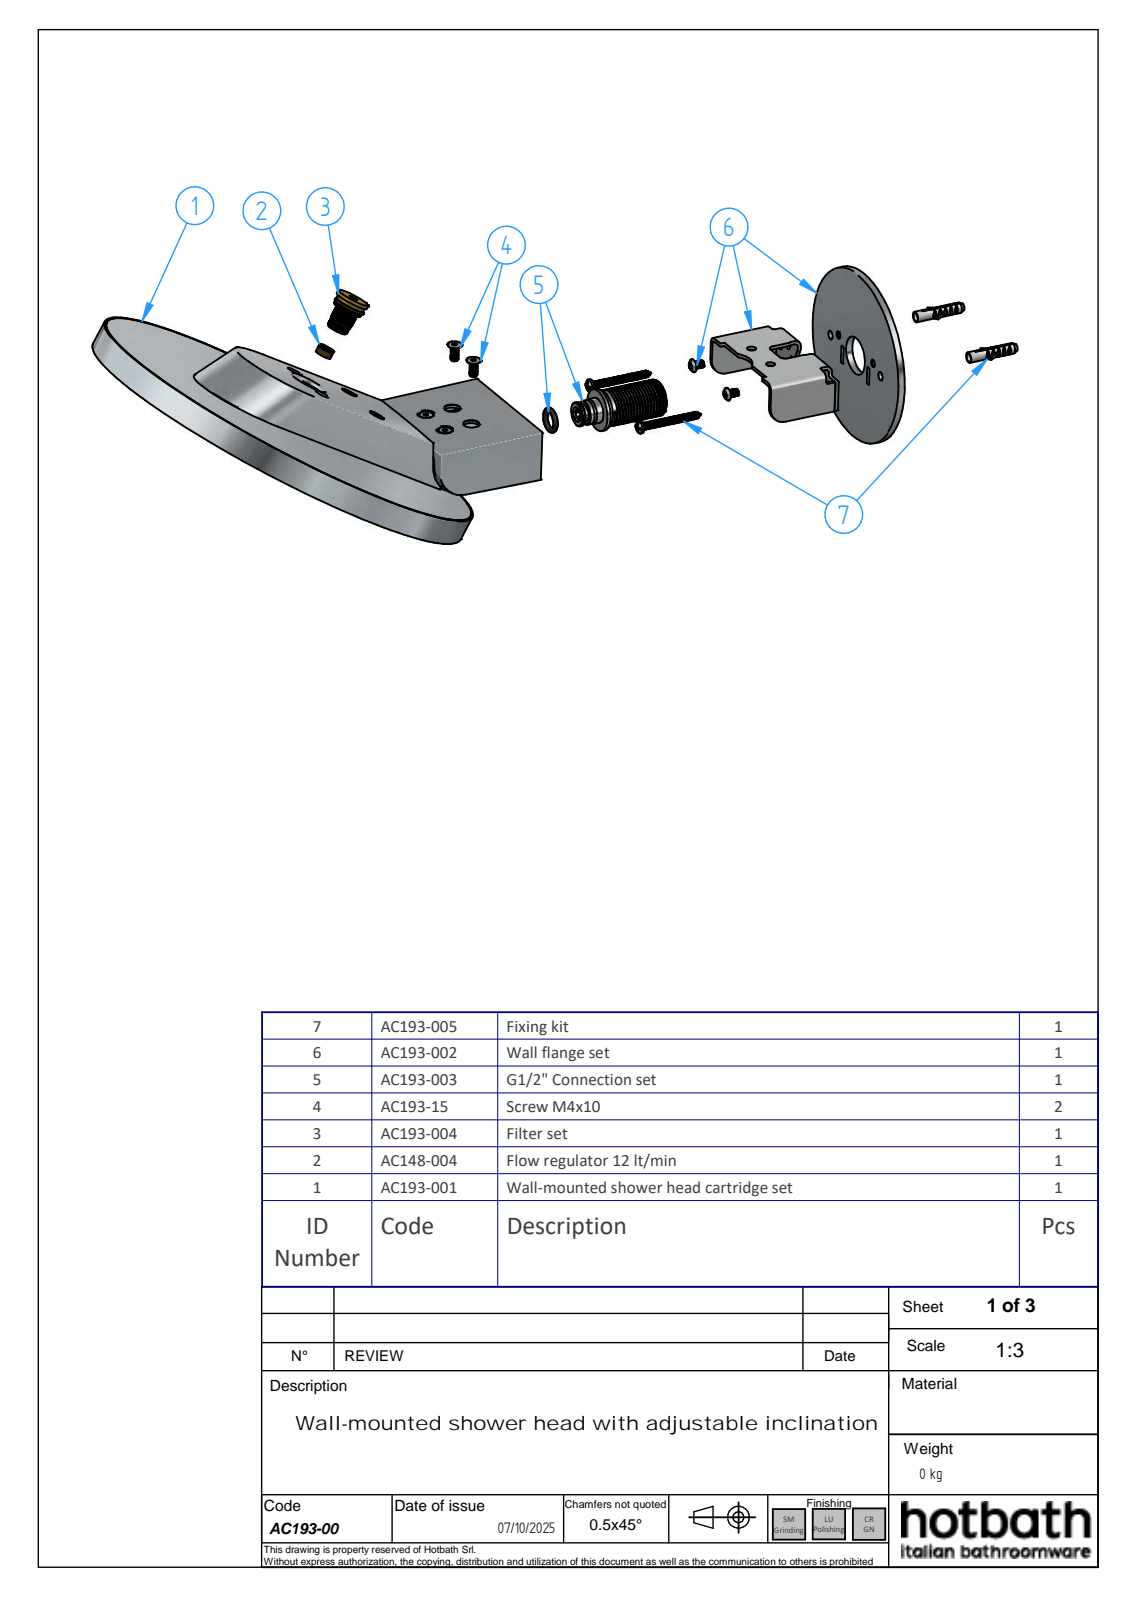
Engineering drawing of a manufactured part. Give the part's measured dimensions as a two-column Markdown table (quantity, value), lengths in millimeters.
| quantity | value |
| --- | --- |
| part name | AC193-00; E044301_28600SC_ASM_1_ASM_oa_0; C073084_068D3ZZ_1; C130044_068D3ZZ_1 (+8 more) |
| STEP written by | Solid Edge (AUTOMOTIVE_DESIGN) |
| units | millimeters |
| bodies | 22 solids, 14013 faces (3144 planar, 1624 cylindrical, 9245 other) |
| overall size | 252.75 × 232 × 143 |
| volume | 689 760 mm³ |
| surface area | 564 044 mm² |
| round holes (diameter × count) | 3.7 × 299, 3.5 × 12, 5 × 9, 3.3 × 6, 4.5 × 6, 4 × 4, 8 × 2, 9 × 2, 8.2 × 1, 9.4 × 1, 10 × 1, 21.4 × 1 |
| round bosses / shafts (diameter × count) | 12.45 × 10, 8.1 × 6, 4 × 6, 7 × 4, 7.3 × 2, 2.9 × 2, 232 × 1, 229.5 × 1 |
| partial cylindrical surfaces (radius × count) | 0.3 × 262, 0.5 × 76, 1 × 25, 0.4 × 24, 1.5 × 20, 0.2 × 16, 0.8 × 12, 0.75 × 8 |
| main face-to-face distances | 1, 14, 9.6, 4.4, 3.4, 3.9, 10.1, 10.6, 13, 11.1 |
| hole center spacings | 30, 32, 35.56, 34.44, 51.8, 64.89, 77.93, 15.03 |
